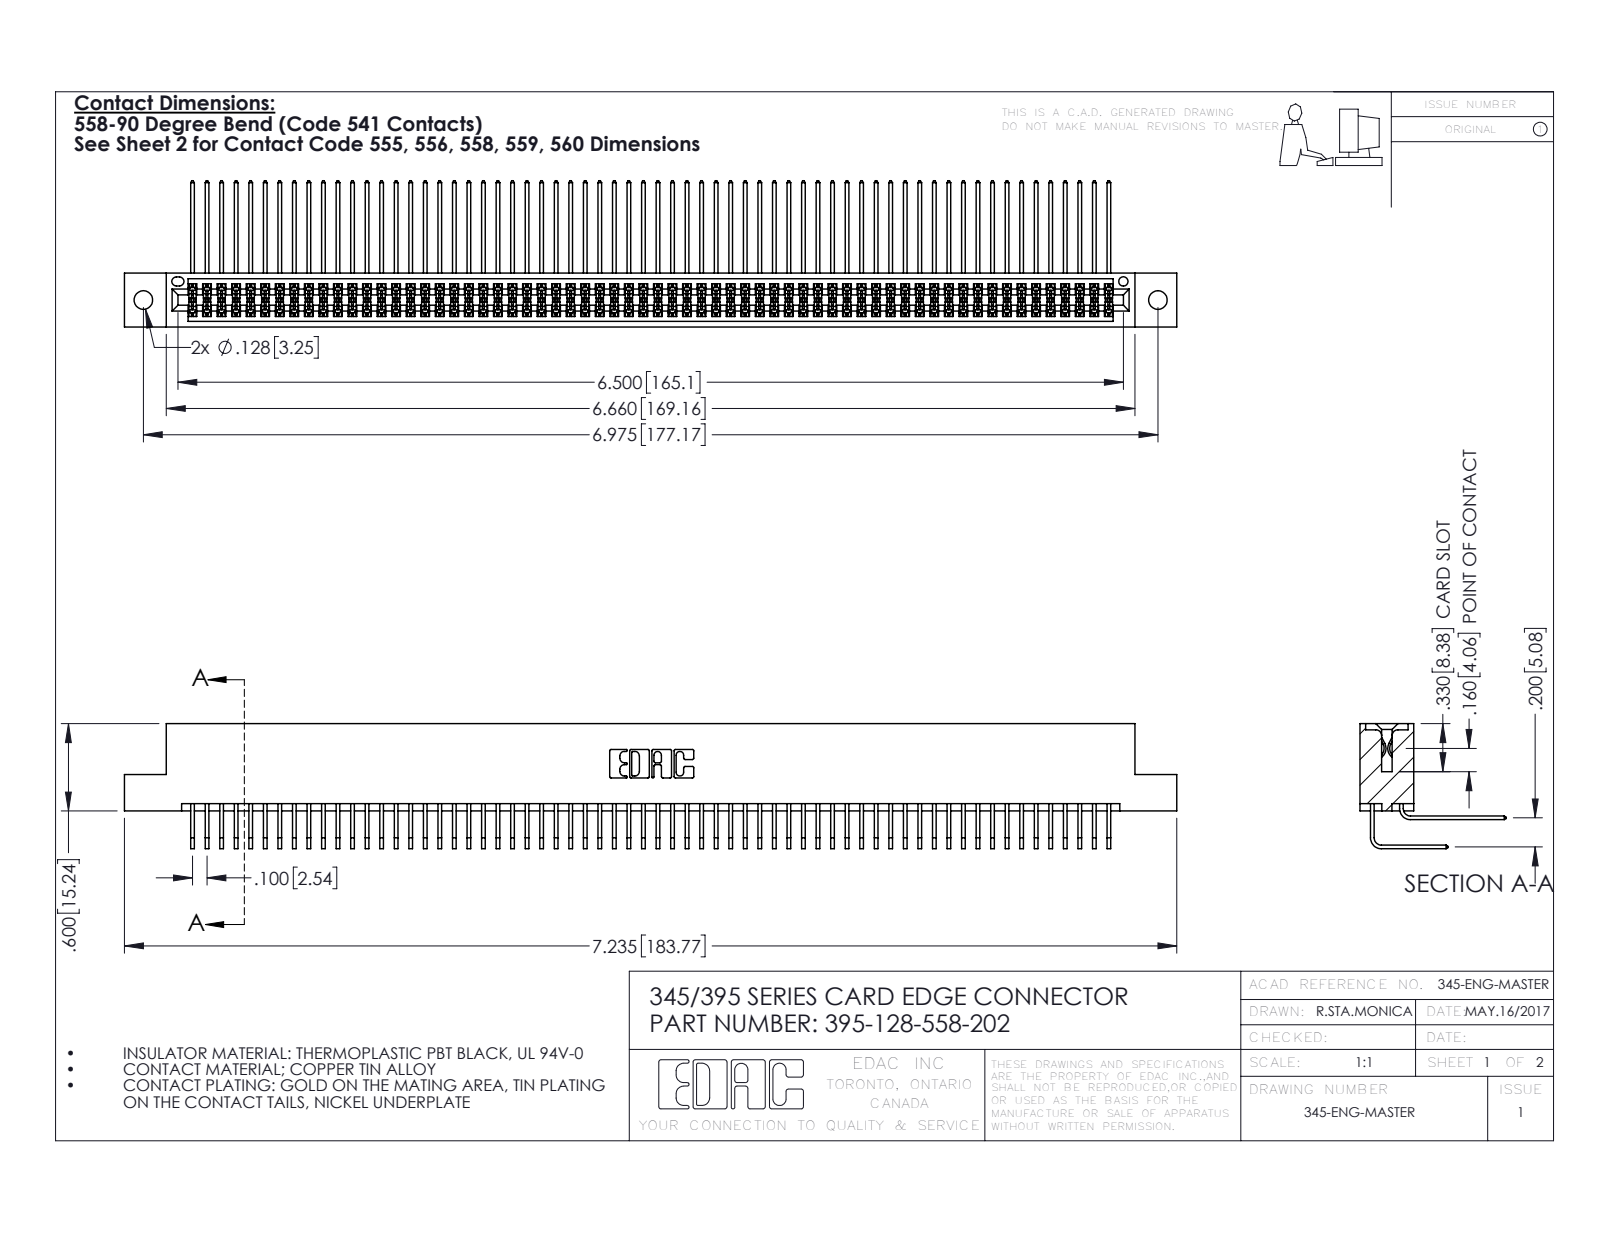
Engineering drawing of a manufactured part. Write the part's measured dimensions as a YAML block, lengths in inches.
part_name: "345-292-001_558 559 Tail - 1; 395-128-558-202; 345 Part_Flush Mounting Lugs - 0.128 Dia; 345-292-001_558 Tail - 2"
step_written_by: "SolidWorks 2016 (CONFIG_CONTROL_DESIGN)"
units: inches
bodies: {solids: 129, faces: 6782, planar: 4560, cylindrical: 2222, other: 0}
overall_size: [7.235, 1.005, 0.859]
volume: 1.145
surface_area: 48.6
round_holes:
  - {diameter: 0.128, count: 2}
  - {diameter: 0.064, count: 1}
partial_cylinders:
  - {radius: 0.006, count: 193}
  - {radius: 0.01, count: 22}
  - {radius: 0.007, count: 6}
  - {radius: 0.031, count: 6}
  - {radius: 0.026, count: 3}
  - {radius: 0.014, count: 2}
  - {radius: 0.019, count: 2}
  - {radius: 0.022, count: 2}
face_to_face_distances: [0.072, 0.298, 0.2, 0.37, 0.098, 0.272, 0.025, 0.225, 0.025, 0.175]
hole_center_spacings: [0.27, 6.739, 6.975]
